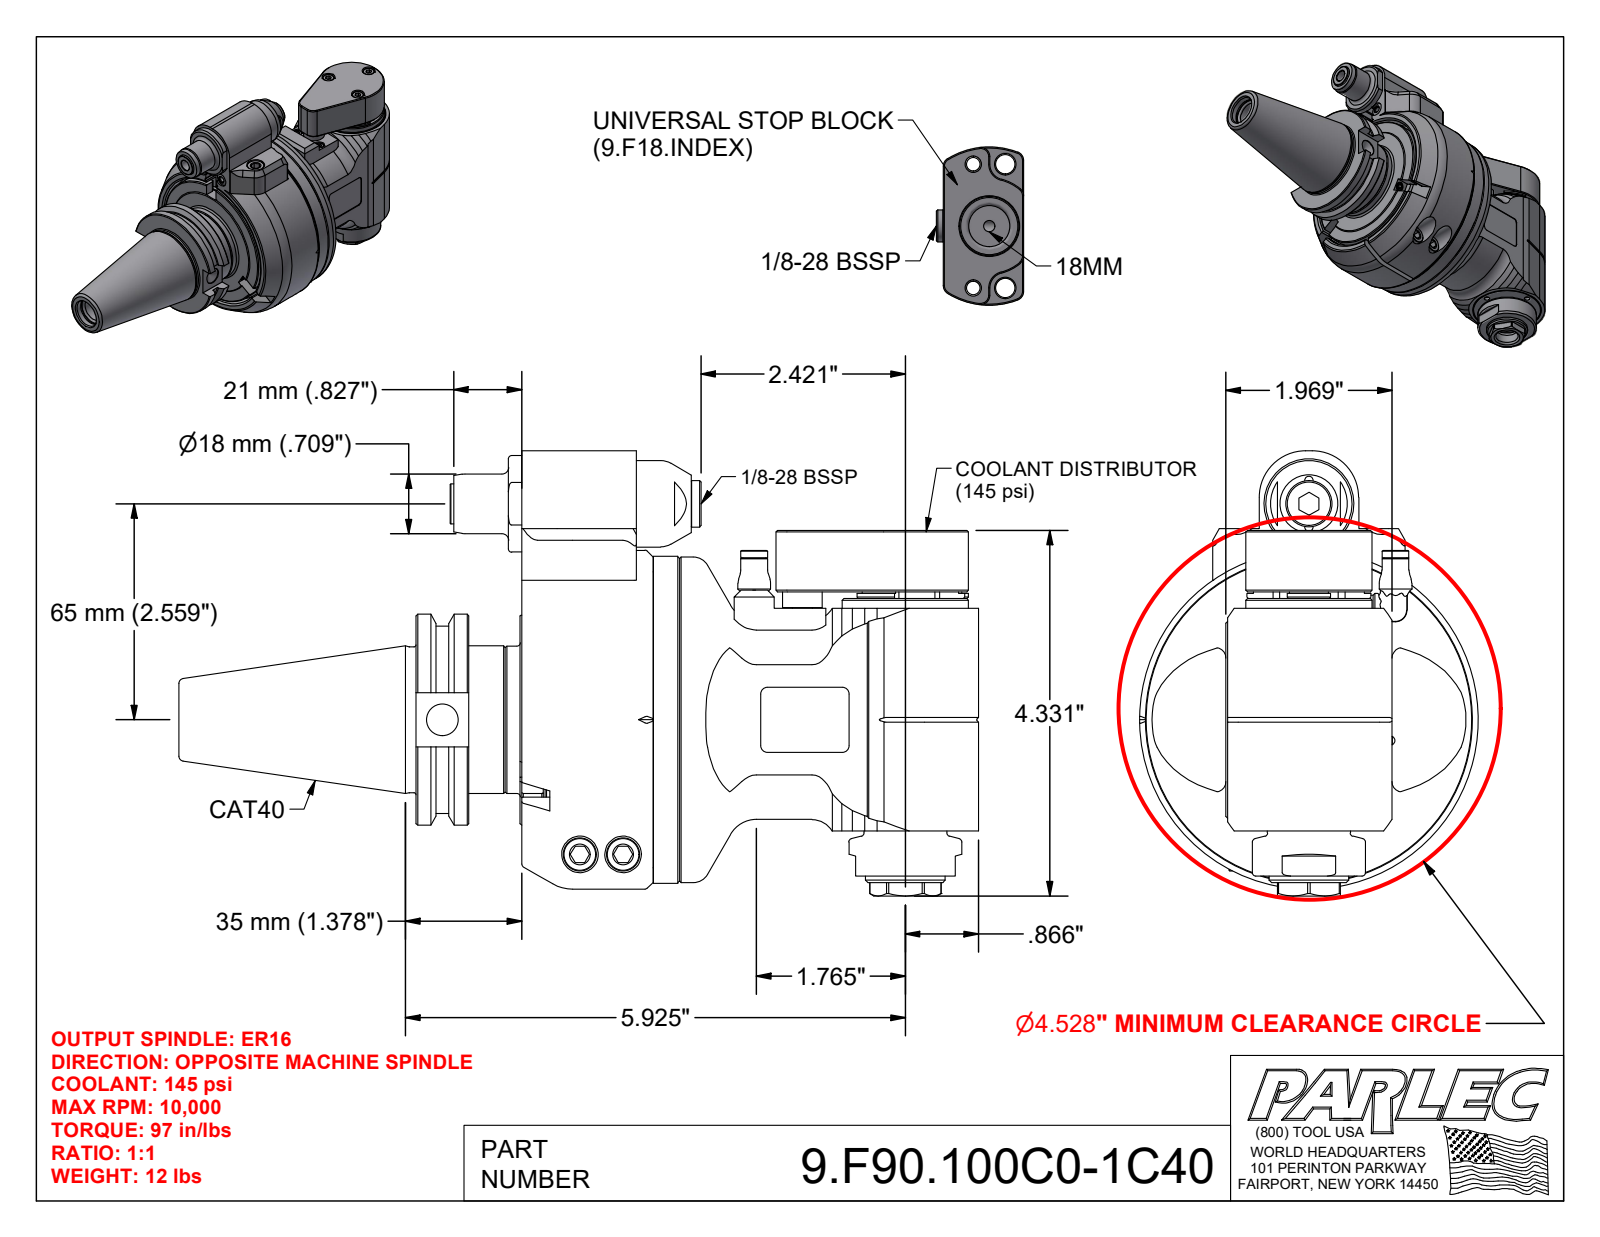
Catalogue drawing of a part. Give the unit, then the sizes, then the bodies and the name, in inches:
Units: inches
Overall size (bounding box): 9.478 × 5.276 × 4.016
Round holes (diameter × count): ⌀0.335 ×20, ⌀0.126 ×8, ⌀0.197 ×3, ⌀0.236 ×3, ⌀0.256 ×3, ⌀0.295 ×3, ⌀0.433 ×3, ⌀0.102 ×2, ⌀0.13 ×2, ⌀0.138 ×2, ⌀0.165 ×2, ⌀0.315 ×2
Round bosses / shafts (diameter × count): ⌀0.394 ×5, ⌀0.472 ×3, ⌀0.276 ×3, ⌀0.236 ×3, ⌀0.709 ×2, ⌀0.315 ×2, ⌀0.217 ×2, ⌀0.098 ×2
Partial cylindrical surfaces — rounded edges, fillets, slot ends (radius × count): R0.039 ×18, R0.079 ×13, R0.118 ×6, R0.02 ×4, R0.157 ×4, R0.006 ×3, R0.016 ×2, R0.138 ×2
Main face-to-face distances: 0.02, 0.039, 0.276, 0.295, 0.335, 1.26, 0.079, 1.555, 1.299, 0.315
Hole centre spacings: 1.516, 2.144, 1.824, 3.002, 0.835, 2.651, 2.914, 3.031
Volume: 51.97 in³ · Surface area: 228.3 in²
Bodies: 4 solids, 901 faces (382 planar, 243 cylindrical, 276 other)
Part name (STEP PRODUCT): 9.F90.100C0-1C40; 9_F90_100B0; 9_GA1_446_2 (EVO, Type 1, C40, 65mm, 35mm)
STEP written by: Autodesk Inventor 2022 (AUTOMOTIVE_DESIGN)
